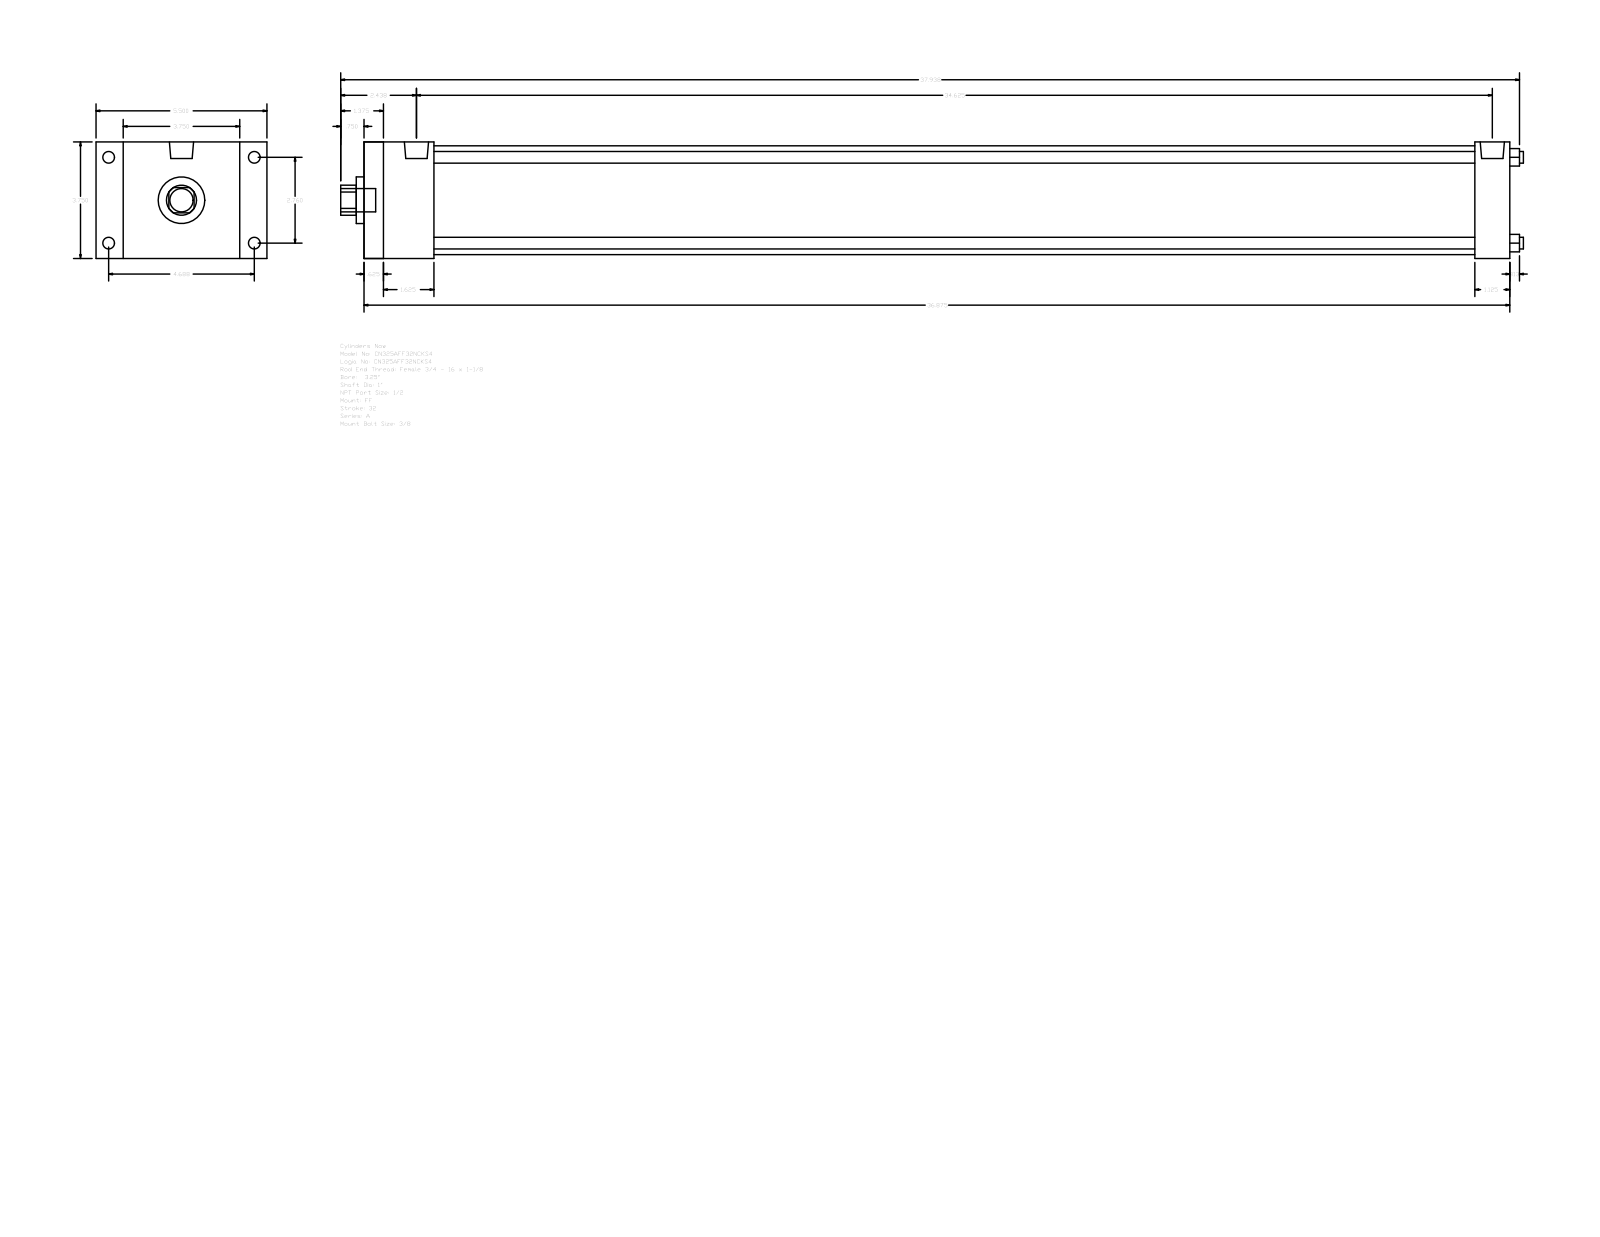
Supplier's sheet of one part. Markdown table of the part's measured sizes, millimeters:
| quantity | value |
| --- | --- |
| part name | A_FF__0325_1 |
| STEP written by | GSSL Pune (CONFIG_CONTROL_DESIGN) |
| units | millimeters |
| bodies | 0 solids, 92 faces (64 planar, 28 cylindrical, 0 other) |
| overall size | 966.79 × 139.7 × 95.25 |
| round holes (diameter × count) | 9.53 × 4, 25.4 × 1, 38.1 × 1, 88.9 × 1 |
| round bosses / shafts (diameter × count) | 9.53 × 4, 8.73 × 4, 19.77 × 2, 19.05 × 1 |
| partial cylindrical surfaces (radius × count) | 12.29 × 1 |
| main face-to-face distances | 95.24, 936.62, 15.87, 920.75, 22.23, 117.47, 28.57, 57.15, 908.05, 41.28 |
| hole center spacings | 49.57, 70.1, 99.14 |
